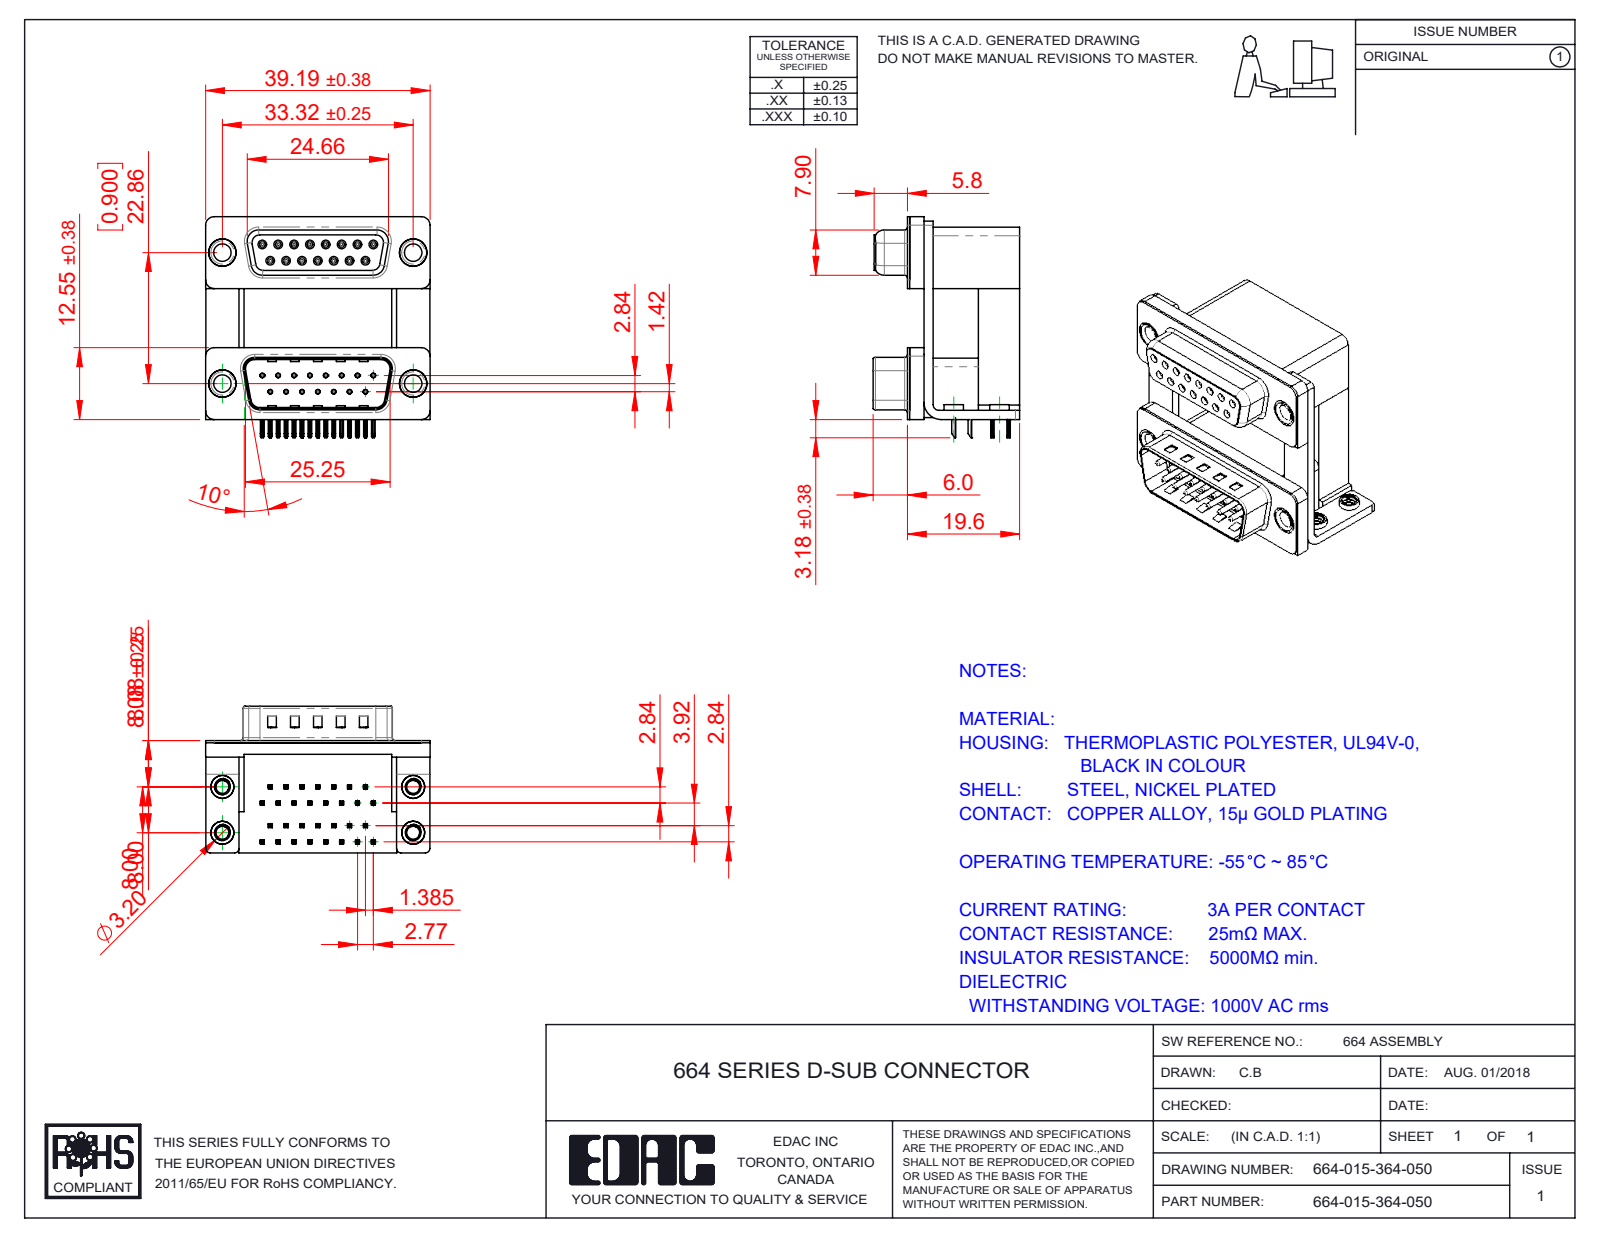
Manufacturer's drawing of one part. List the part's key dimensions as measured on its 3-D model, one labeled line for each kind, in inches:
Part name (STEP PRODUCT): 664 Contact Top Lower; 664 Mounting Bracket_ThruH; 664 4-40 Threaded Board Mount; 664 Contact Bottom Upper_H (+8 more)
STEP written by: SolidWorks 2020 (CONFIG_CONTROL_DESIGN)
Units: inches
Bodies: 45 solids, 3968 faces (2027 planar, 1054 cylindrical, 887 other)
Overall size (bounding box): 1.543 × 1.519 × 1.008
Volume: 0.973 in³ · Surface area: 27.53 in²
Round holes (diameter × count): ⌀0.031 ×30, ⌀0.014 ×15, ⌀0.035 ×15, ⌀0.089 ×4, ⌀0.108 ×4, ⌀0.12 ×4, ⌀0.126 ×4, ⌀0.138 ×4, ⌀0.157 ×4, ⌀0.189 ×4, ⌀0.197 ×4
Round bosses / shafts (diameter × count): ⌀0.047 ×15, ⌀0.03 ×15, ⌀0.193 ×4, ⌀0.187 ×4, ⌀0.157 ×4, ⌀0.152 ×4, ⌀0.134 ×4
Partial cylindrical surfaces — rounded edges, fillets, slot ends (radius × count): R0.004 ×120, R0.006 ×60, R0.01 ×60, R0.005 ×30, R0.014 ×30, R0.059 ×16, R0.013 ×15, R0.02 ×12
Main face-to-face distances: 0.016, 0.756, 0.472, 0.283, 0.657, 0.374, 0.098, 0.086, 0.488, 0.9
Hole centre spacings: 0.124, 0.109, 0.907, 0.218, 0.926, 0.327, 0.9, 0.957
